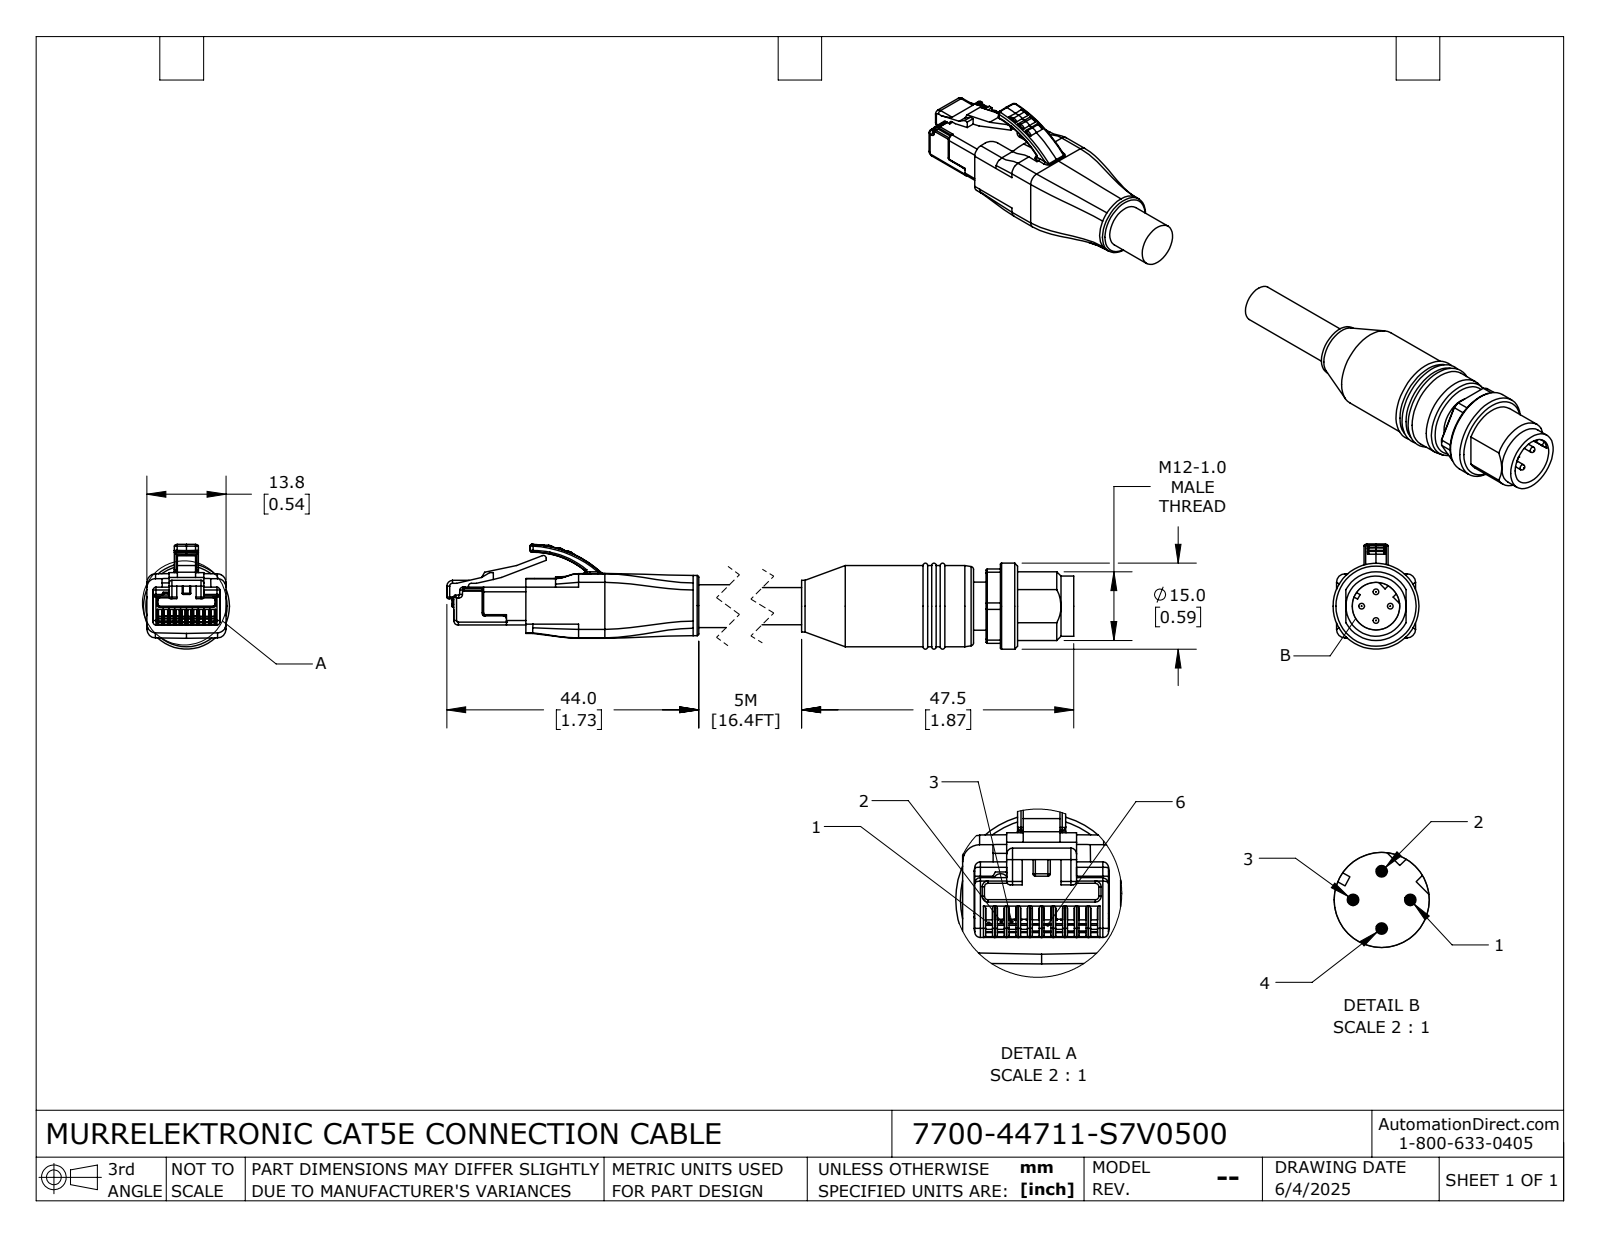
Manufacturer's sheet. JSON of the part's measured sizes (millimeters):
{"part_name": "7700-44711-S7V0500; 7700-44711-S7V0500_RJ45; 7700-44711-S7V0500_MALE", "step_written_by": "SolidWorks 2024 (CONFIG_CONTROL_DESIGN)", "units": "millimeters", "bodies": {"solids": 2, "faces": 757, "planar": 357, "cylindrical": 235, "other": 165}, "overall_size": [144.5, 18.29, 15], "volume_mm3": 11873, "surface_area_mm2": 5775, "round_holes": [[8.3, 1]], "round_bosses_or_shafts": [[1, 4], [10.5, 2], [15, 1], [14.2, 1], [9, 1], [8.4, 1], [7.5, 1], [6.5, 1]], "partial_cylinders_radius": [[0.2, 61], [0.5, 25], [0.3, 14], [1.5, 9], [0.8, 5], [0.54, 2], [5, 2], [0.13, 1]], "face_to_face_distances": [13.8, 2.2, 1.65, 12.15, 1.01, 12.79, 0.64, 11.14, 9.8, 0.9]}
